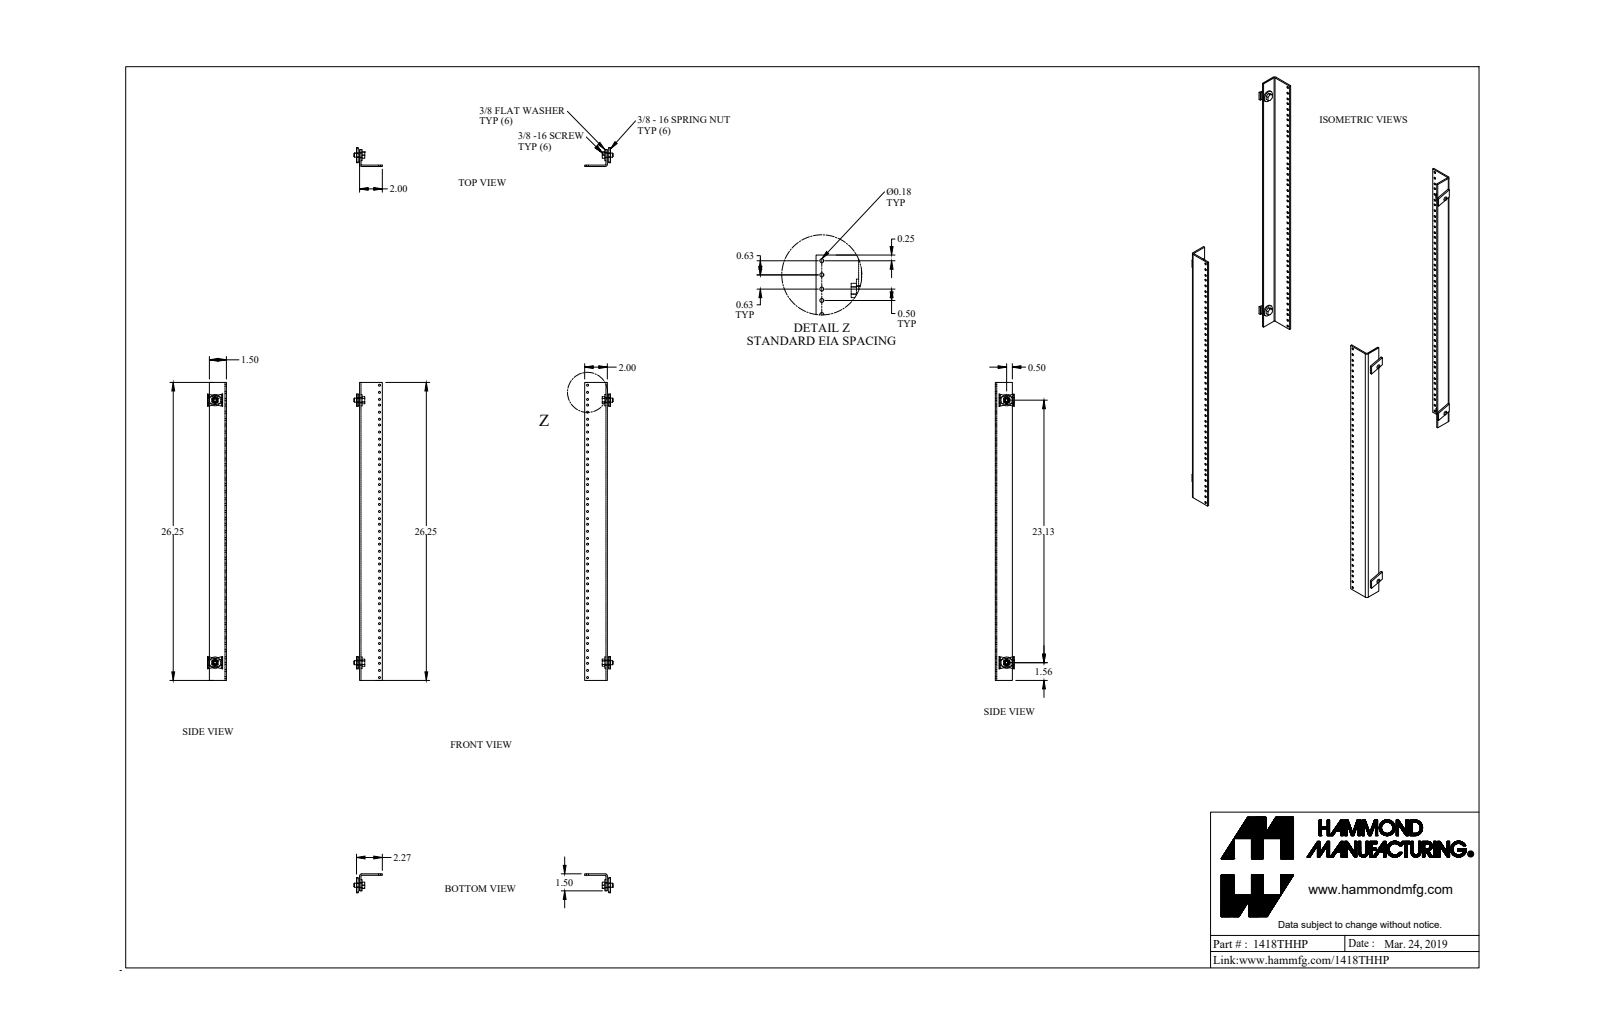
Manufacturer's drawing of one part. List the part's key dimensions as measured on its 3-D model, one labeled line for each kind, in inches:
Part name (STEP PRODUCT): 1418THHP_Default
STEP written by: SolidWorks 2019 (CONFIG_CONTROL_DESIGN)
Units: inches
Bodies: 14 solids, 356 faces (124 planar, 224 cylindrical, 8 other)
Overall size (bounding box): 26.25 × 22.856 × 1.668
Volume: 22.78 in³ · Surface area: 389.7 in²
Round holes (diameter × count): ⌀0.177 ×90, ⌀0.313 ×2, ⌀0.437 ×2, ⌀0.445 ×2
Round bosses / shafts (diameter × count): ⌀1 ×2, ⌀0.36 ×2
Partial cylindrical surfaces — rounded edges, fillets, slot ends (radius × count): R0.06 ×2, R0.185 ×2
Main face-to-face distances: 0.125, 0.125, 21.84, 21.59, 21.715, 21.715, 1.5, 1.375, 1.375, 2
Hole centre spacings: 1.75, 3.5, 2.375, 7, 0.625, 4.125, 5.25, 1.125
